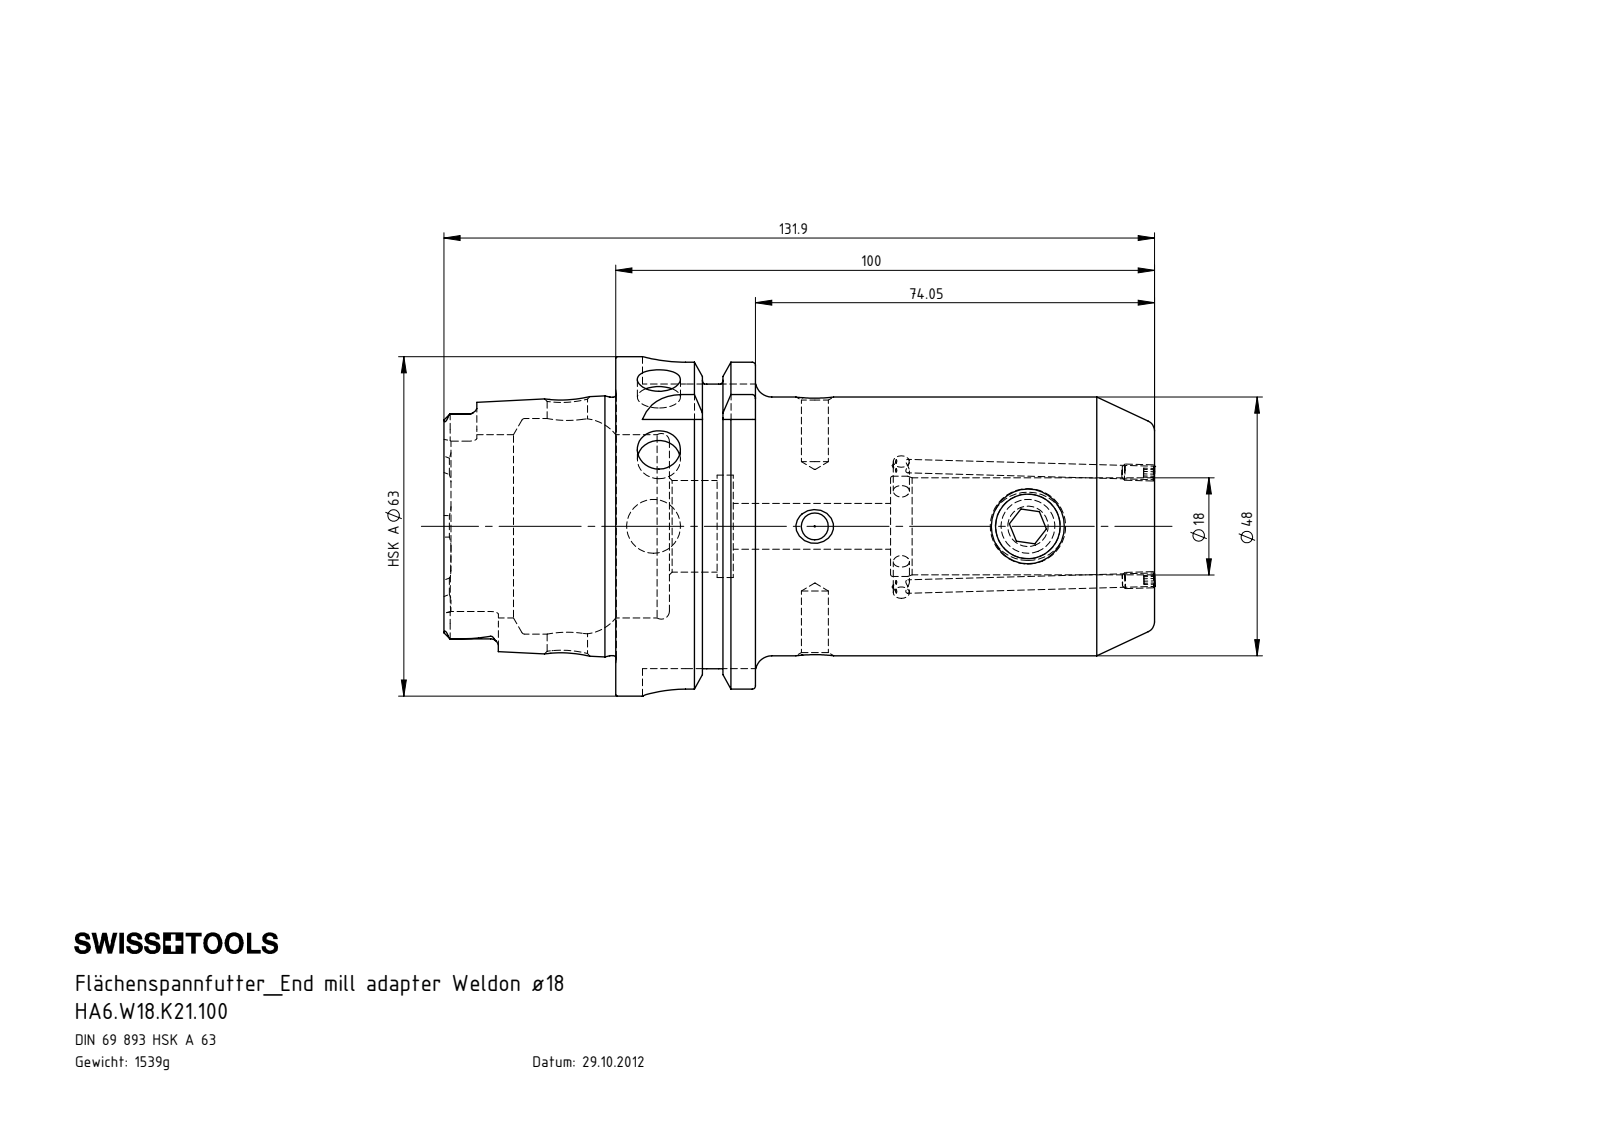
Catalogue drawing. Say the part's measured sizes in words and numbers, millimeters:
The part is named "HA6-W18.K21.100; ERU-CJ2.001.006; W16-ER1.001.016; HA6-W18.K21.100_A_Fertigbearbeitung". Its 3-D file was written by "SolidWorks 2012 (CONFIG_CONTROL_DESIGN)". It is 4 solids with 292 faces: 78 planar, 86 cylindrical and 128 other. Overall it measures 131.98 by 63 by 63 millimeters. Its volume is 196 010 cubic millimeters and its surface area 39 351 square millimeters. Round holes: 2 of diameter 2.5, 2 of diameter 5, 2 of diameter 8, 1 of diameter 3, 1 of diameter 7.5, 1 of diameter 8.5, 1 of diameter 10, 1 of diameter 12, 1 of diameter 17, 1 of diameter 18, 1 of diameter 18.6, 1 of diameter 19. Round bosses or shafts: 2 of diameter 3, 1 of diameter 63, 1 of diameter 54.95, 1 of diameter 48, 1 of diameter 47.94, 1 of diameter 14. Partial cylindrical surfaces (rounded edges, fillets, slot ends): 6 of radius 1.4, 4 of radius 2.88, 4 of radius 8, 1 of radius 10.56. The main face-to-face distances are 100, 25.95, 74.05, 16, 9.95, 90.05, 31.9, 41.85, 57.85, 131.9. The hole center spacings are 29.95, 39.55, 45.95, 69.5.
